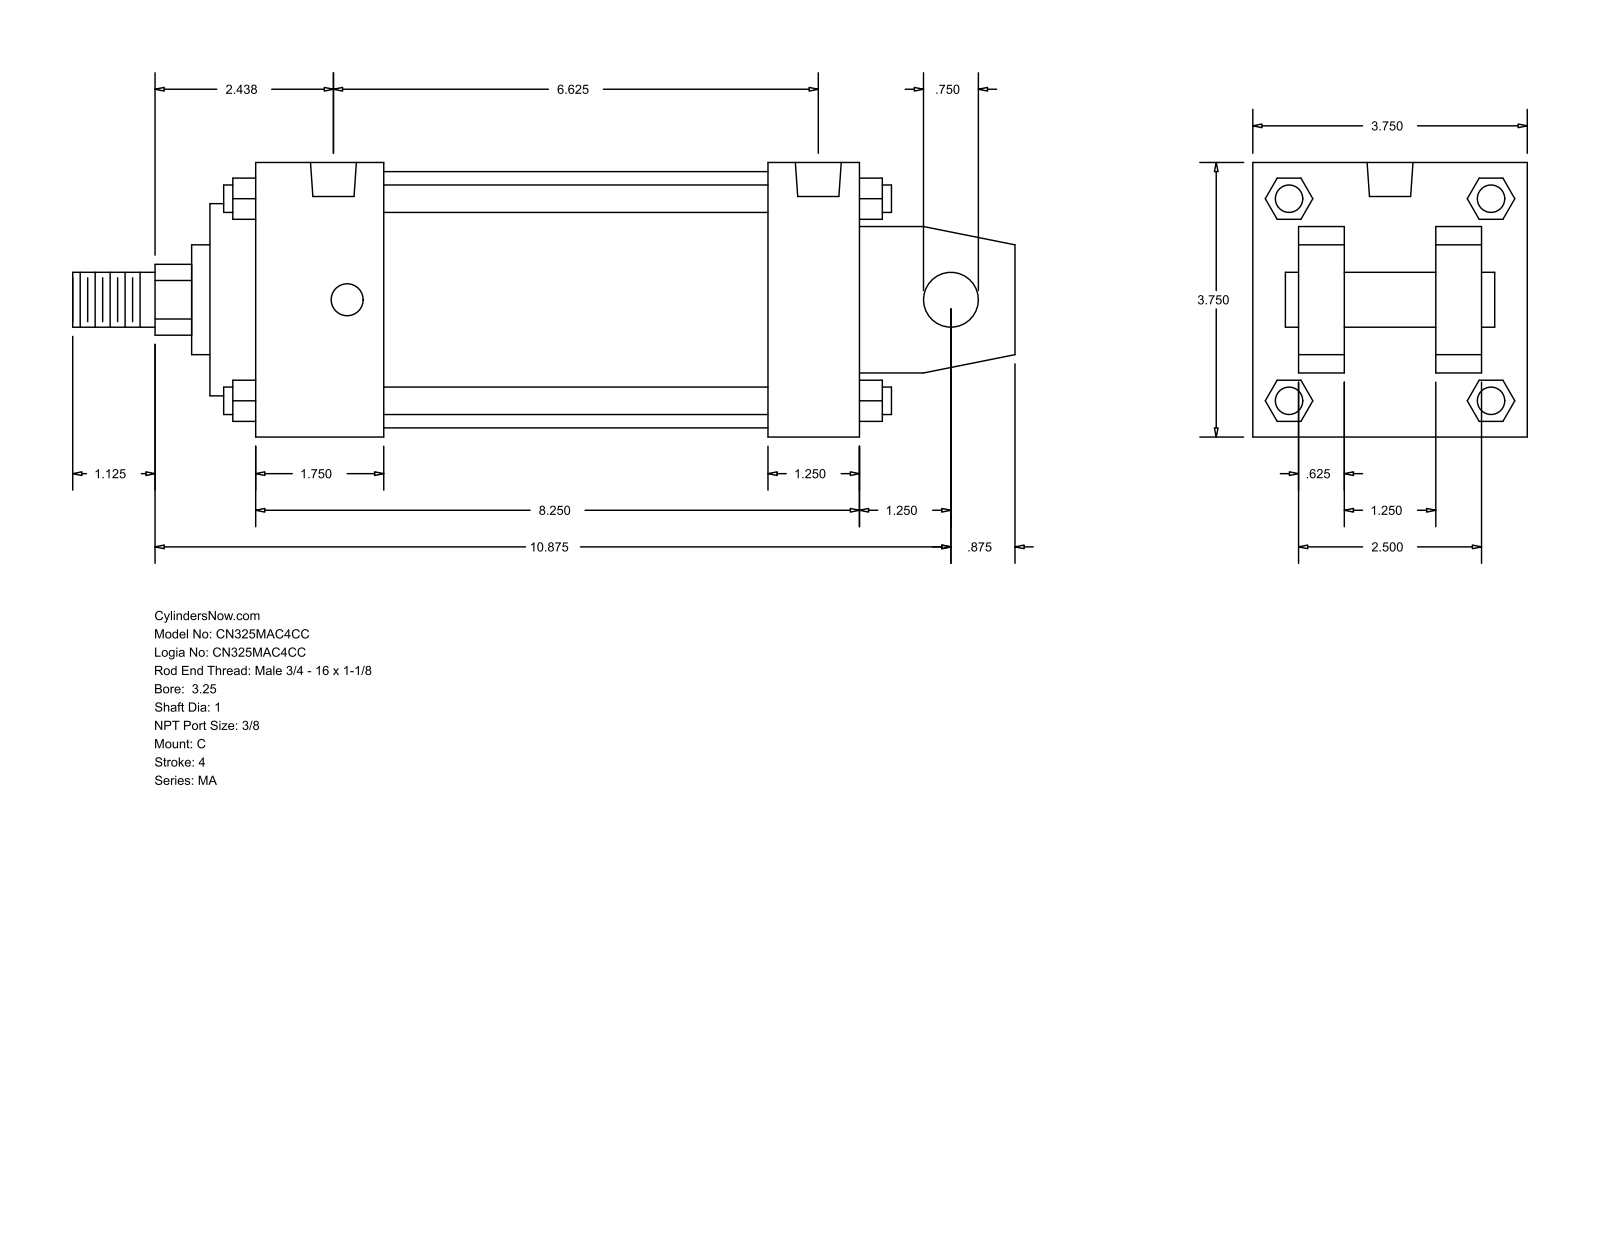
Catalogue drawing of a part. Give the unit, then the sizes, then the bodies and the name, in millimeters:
Units: millimetres
Overall size (bounding box): 327.02 × 95.25 × 95.25
Round holes (diameter × count): ⌀11.11 ×4, ⌀15.93 ×2
Round bosses / shafts (diameter × count): ⌀9.53 ×4, ⌀19.05 ×2, ⌀88.9 ×1, ⌀66.67 ×1, ⌀38.1 ×1, ⌀25.4 ×1
Partial cylindrical surfaces — rounded edges, fillets, slot ends (radius × count): R12.29 ×1
Main face-to-face distances: 95.24, 15.87, 63.5, 209.55, 31.74, 79.37, 47.63, 225.42, 177.8, 31.75
Hole centre spacings: 4.76, 158.76, 163.52, 168.28
Bodies: 0 solids, 141 faces (109 planar, 32 cylindrical, 0 other)
Part name (STEP PRODUCT): MA_C__0325_1
STEP written by: GSSL Pune (CONFIG_CONTROL_DESIGN)
